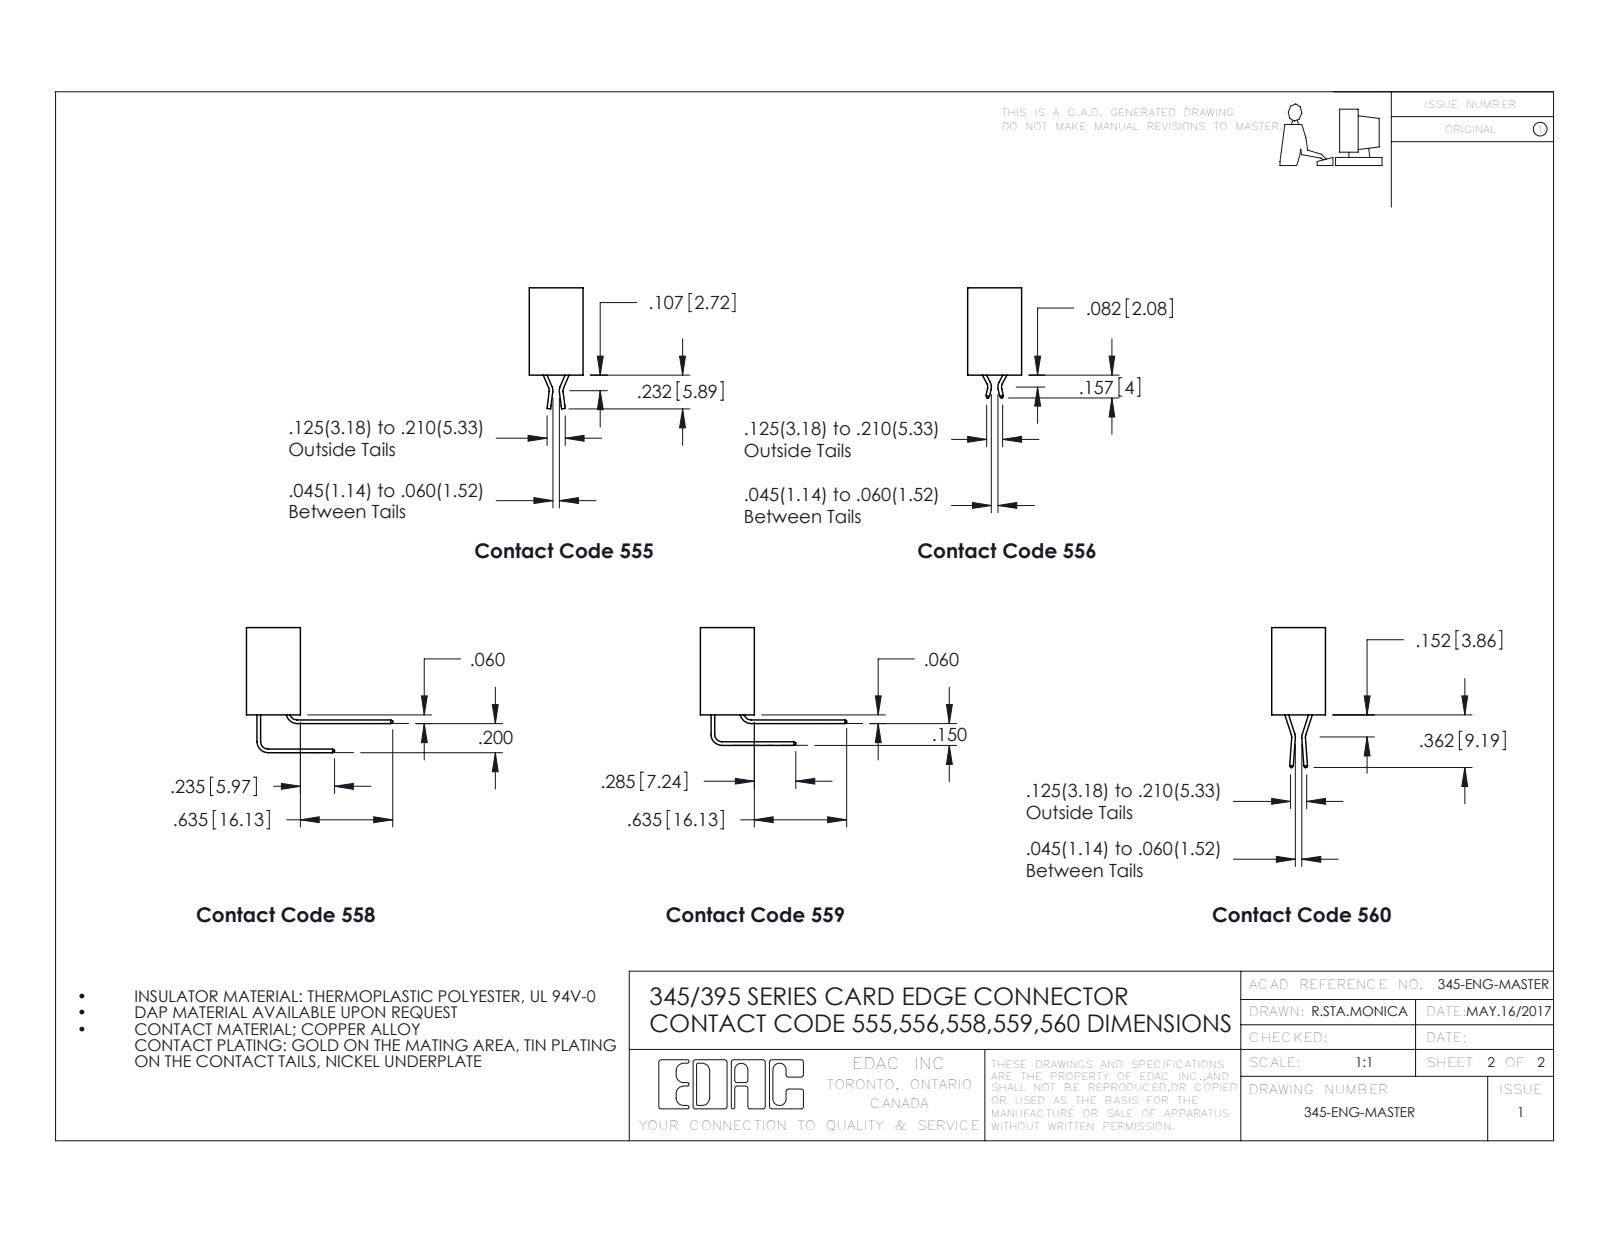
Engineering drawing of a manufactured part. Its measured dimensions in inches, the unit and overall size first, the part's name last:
Units: inches
Overall size (bounding box): 0.76 × 0.737 × 0.37
Round holes (diameter × count): ⌀0.064 ×1
Partial cylindrical surfaces — rounded edges, fillets, slot ends (radius × count): R0.01 ×22, R0.006 ×10, R0.007 ×6, R0.031 ×6, R0.026 ×3, R0.031 ×2, R0.04 ×2, R0.014 ×1
Main face-to-face distances: 0.2, 0.1, 0.37, 0.298, 0.072, 0.06, 0.025, 0.76, 0.55, 0.098
Volume: 0.128 in³ · Surface area: 3.724 in²
Bodies: 6 solids, 428 faces (306 planar, 122 cylindrical, 0 other)
Part name (STEP PRODUCT): 345 Part_No Mounting Lugs; 345-005-525-101; 345-292-001_345-293-125
STEP written by: SolidWorks 2020 (CONFIG_CONTROL_DESIGN)
